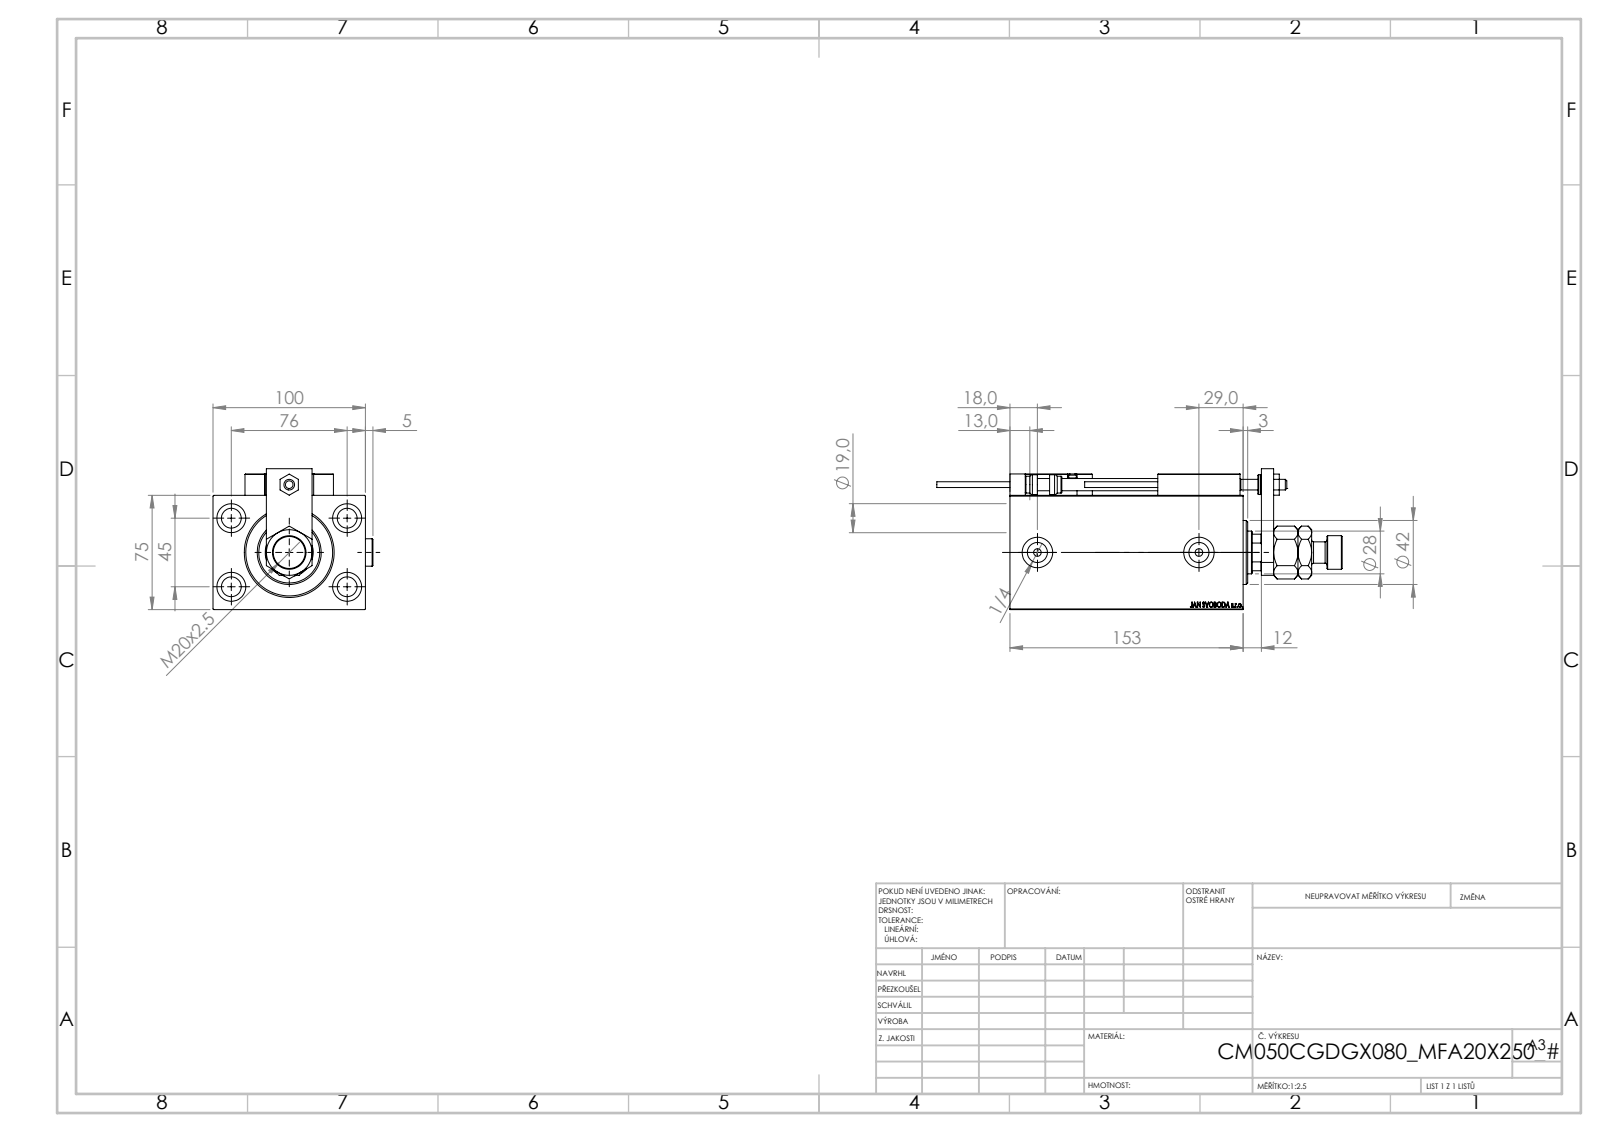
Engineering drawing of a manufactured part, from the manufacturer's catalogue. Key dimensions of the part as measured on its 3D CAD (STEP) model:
Part name (STEP PRODUCT): NUT_D12; MAGNET; V450CM_VC_B; X_Y_MFA (+7 more)
STEP written by: SolidWorks 2019 (CONFIG_CONTROL_DESIGN)
Units: millimetres
Bodies: 26 solids, 1391 faces (611 planar, 210 cylindrical, 570 other)
Overall size (bounding box): 266 × 104.9 × 92.5
Volume: 1 021 000 mm³ · Surface area: 183 850 mm²
Round holes (diameter × count): ⌀8 ×5, ⌀3.2 ×4, ⌀4 ×4, ⌀5 ×4, ⌀13 ×4, ⌀19 ×4, ⌀20 ×3, ⌀13.16 ×2, ⌀7 ×1, ⌀18.5 ×1, ⌀28 ×1, ⌀31.5 ×1
Round bosses / shafts (diameter × count): ⌀18 ×2, ⌀5 ×2, ⌀3.8 ×2, ⌀42 ×1, ⌀22 ×1, ⌀14 ×1, ⌀13 ×1, ⌀11 ×1
Partial cylindrical surfaces — rounded edges, fillets, slot ends (radius × count): R0.3 ×30, R3 ×2, R13.5 ×1
Main face-to-face distances: 75, 100, 14, 153, 12, 139, 20, 8, 24, 25
Hole centre spacings: 44.16, 11.37, 20, 29.59, 29.69, 36.06, 42.19, 43.91
